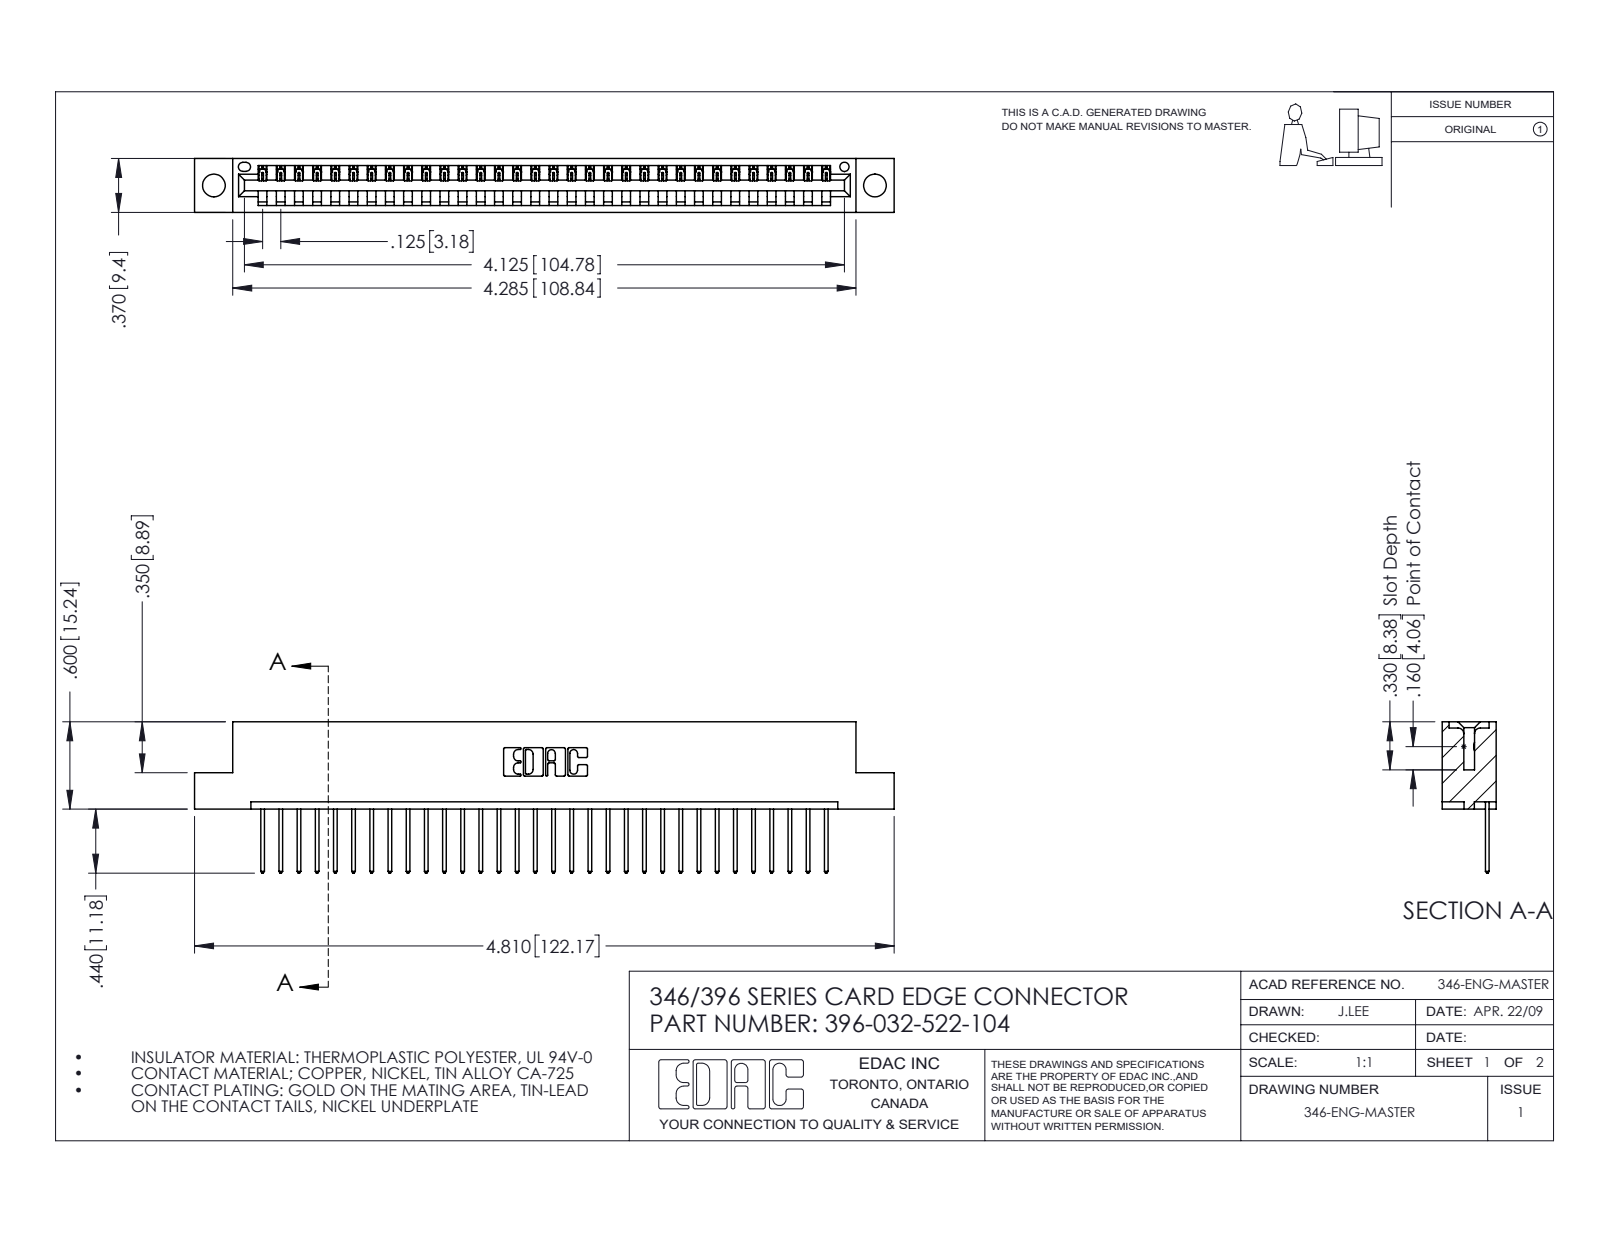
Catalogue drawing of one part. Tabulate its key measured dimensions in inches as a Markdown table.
| quantity | value |
| --- | --- |
| part name | 396-032-522-104; 345-292-001_345-293-122; 346 Part_Flush Mounting Lugs - 0.156 Dia-TH |
| STEP written by | SolidWorks 2016 (CONFIG_CONTROL_DESIGN) |
| units | inches |
| bodies | 33 solids, 1978 faces (1356 planar, 622 cylindrical, 0 other) |
| overall size | 4.81 × 1.04 × 0.37 |
| volume | 0.704 in³ |
| surface area | 22.07 in² |
| round holes (diameter × count) | 0.156 × 2, 0.064 × 1 |
| partial cylindrical surfaces (radius × count) | 0.006 × 64, 0.01 × 64, 0.01 × 22, 0.007 × 6, 0.031 × 6, 0.026 × 3, 0.031 × 2, 0.04 × 2 |
| main face-to-face distances | 0.048, 0.322, 0.37, 0.25, 0.072, 0.298, 0.025, 0.148, 0.222, 0.1 |
| hole center spacings | 0.246, 4.337, 4.545 |
